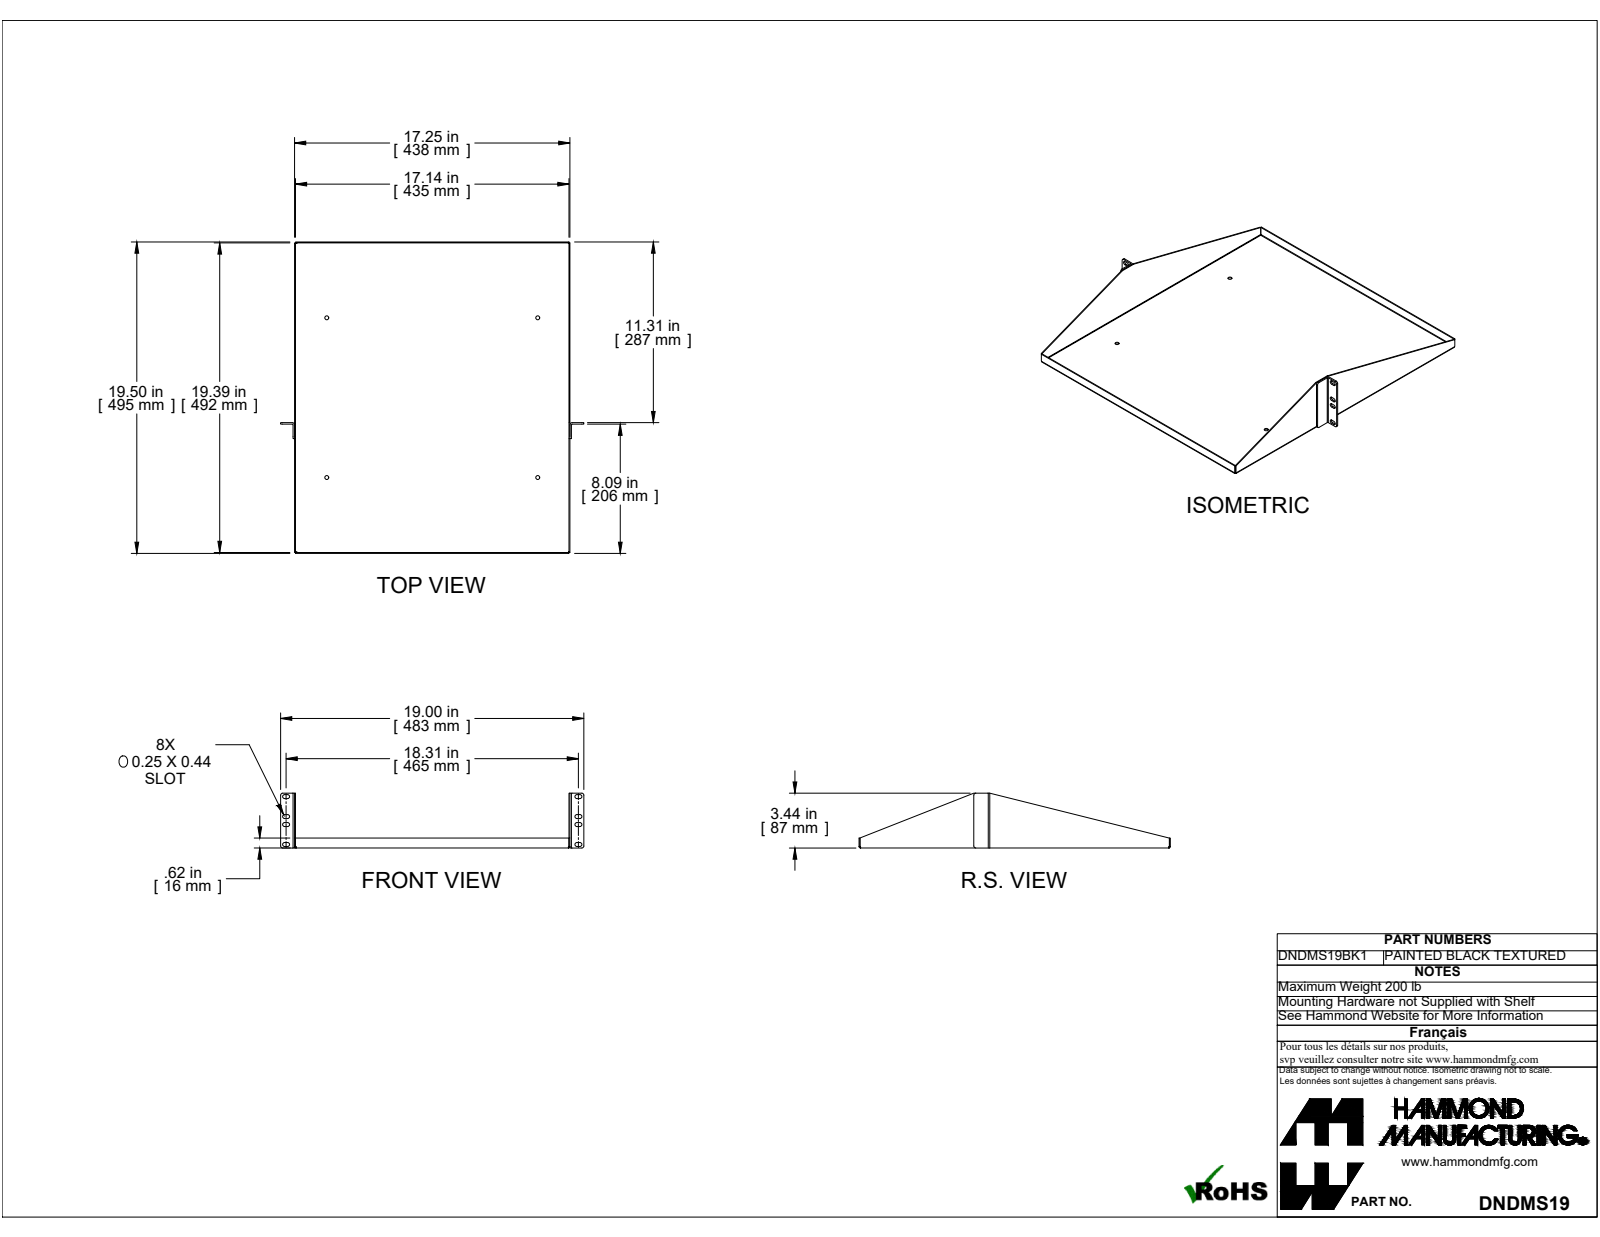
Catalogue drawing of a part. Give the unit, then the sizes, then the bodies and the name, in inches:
Units: inches
Overall size (bounding box): 19.5 × 19 × 3.437
Round holes (diameter × count): ⌀0.25 ×4
Partial cylindrical surfaces — rounded edges, fillets, slot ends (radius × count): R0.125 ×22, R0.029 ×4, R0.055 ×4, R0.086 ×4, R0.048 ×2, R0.143 ×2
Main face-to-face distances: 0.057, 0.057, 17.193, 17.25, 17.136, 19.443, 0.095, 19.386, 19.5, 0.152
Hole centre spacings: 10, 13.218, 16.575
Volume: 25.75 in³ · Surface area: 896 in²
Bodies: 3 solids, 114 faces (58 planar, 48 cylindrical, 8 other)
Part name (STEP PRODUCT): DNDMS19BK1
STEP written by: SolidWorks 2019 (CONFIG_CONTROL_DESIGN)
